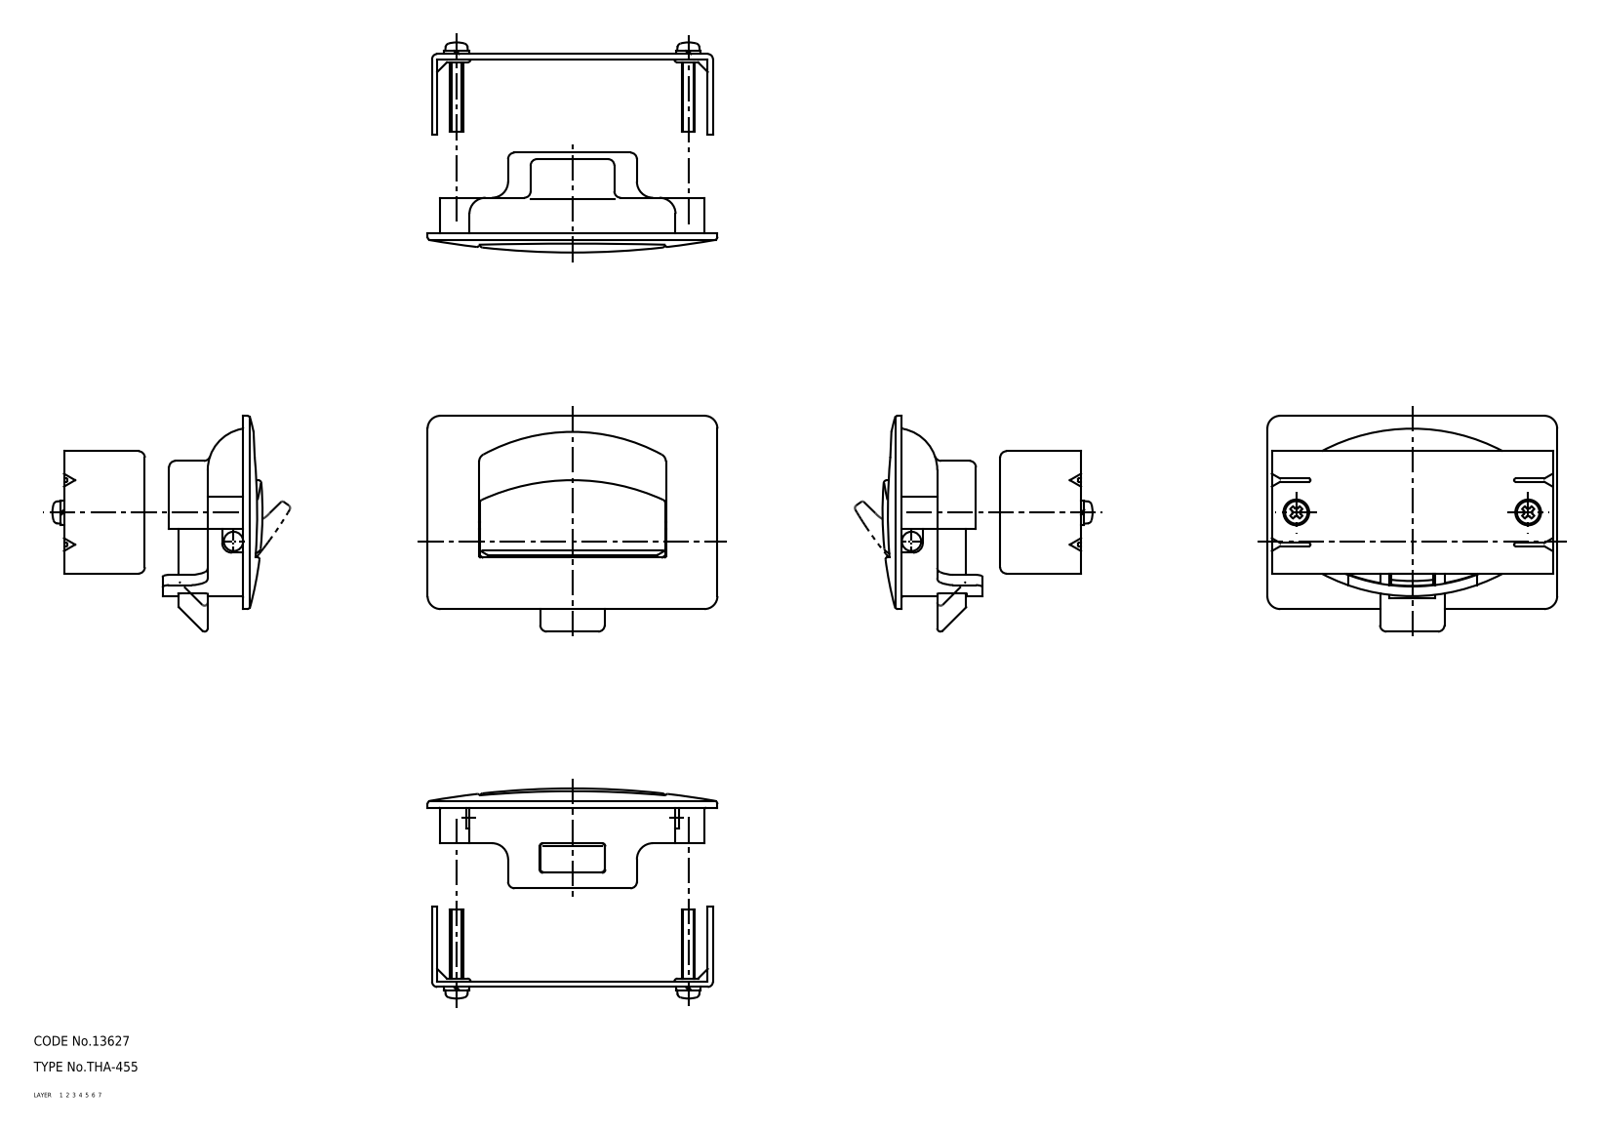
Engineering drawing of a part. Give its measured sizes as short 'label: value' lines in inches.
name: 67132205; 67132218; 67132231; 67132244
written by: CADfix (AUTOMOTIVE_DESIGN)
unit: in
bodies: 4 solids, 414 faces (0 planar, 0 cylindrical, 414 other)
size: 3.543 × 2.638 × 1.403
volume: 2.854 in³; area: 59.36 in²
